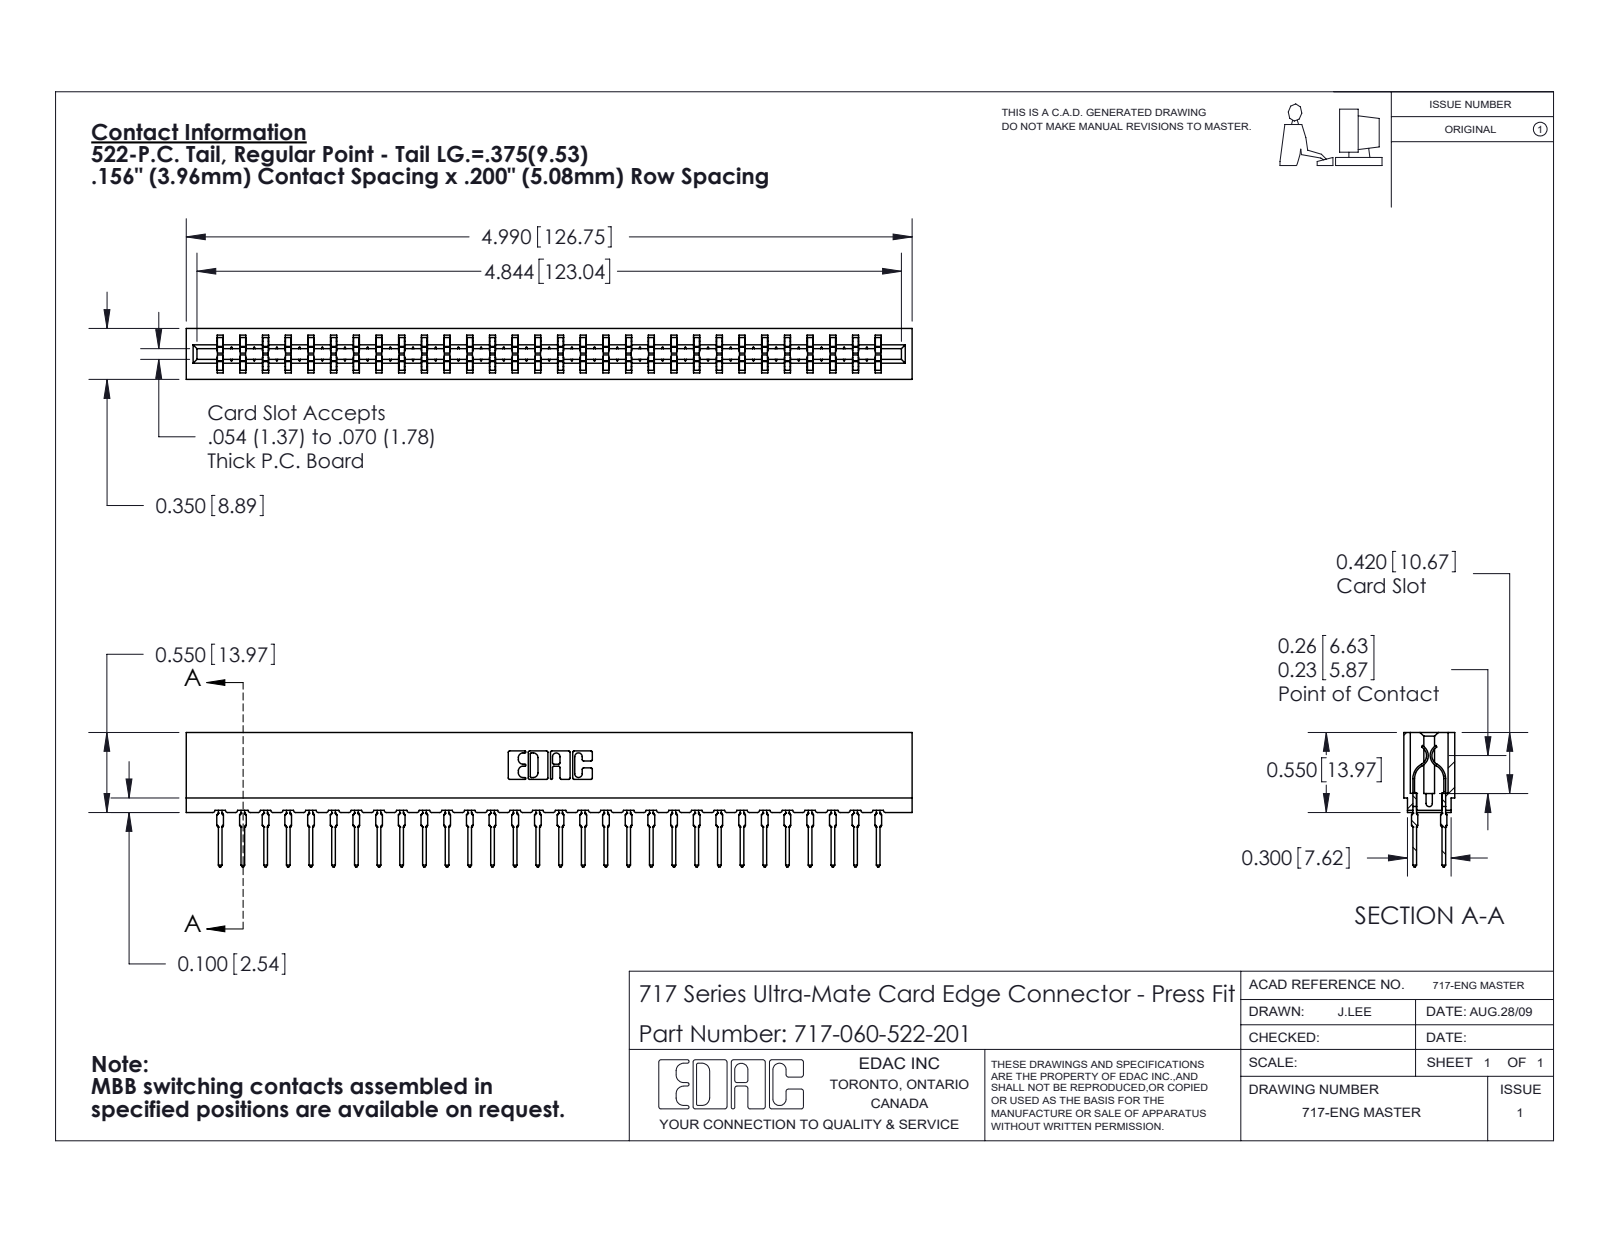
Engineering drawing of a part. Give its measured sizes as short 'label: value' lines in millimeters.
name: 717 Part_Insulator Option - 06; 745-292-001_522; 717-060-522-201
written by: SolidWorks 2020 (CONFIG_CONTROL_DESIGN)
unit: mm
bodies: 61 solids, 5494 faces (2844 planar, 1090 cylindrical, 1560 other)
size: 126.7 × 23.5 × 8.9
volume: 11 100 mm³; area: 17 050 mm²
rounds: 120× R0.5, 60× R0.4, 22× R0.3, 8× R0.1, 8× R0.3, 6× R0.2, 6× R0.8, 3× R0.7
face distances: 5.4, 3.5, 8.9, 1.6, 7.3, 1.9, 3.8, 1.9, 4, 1.1
